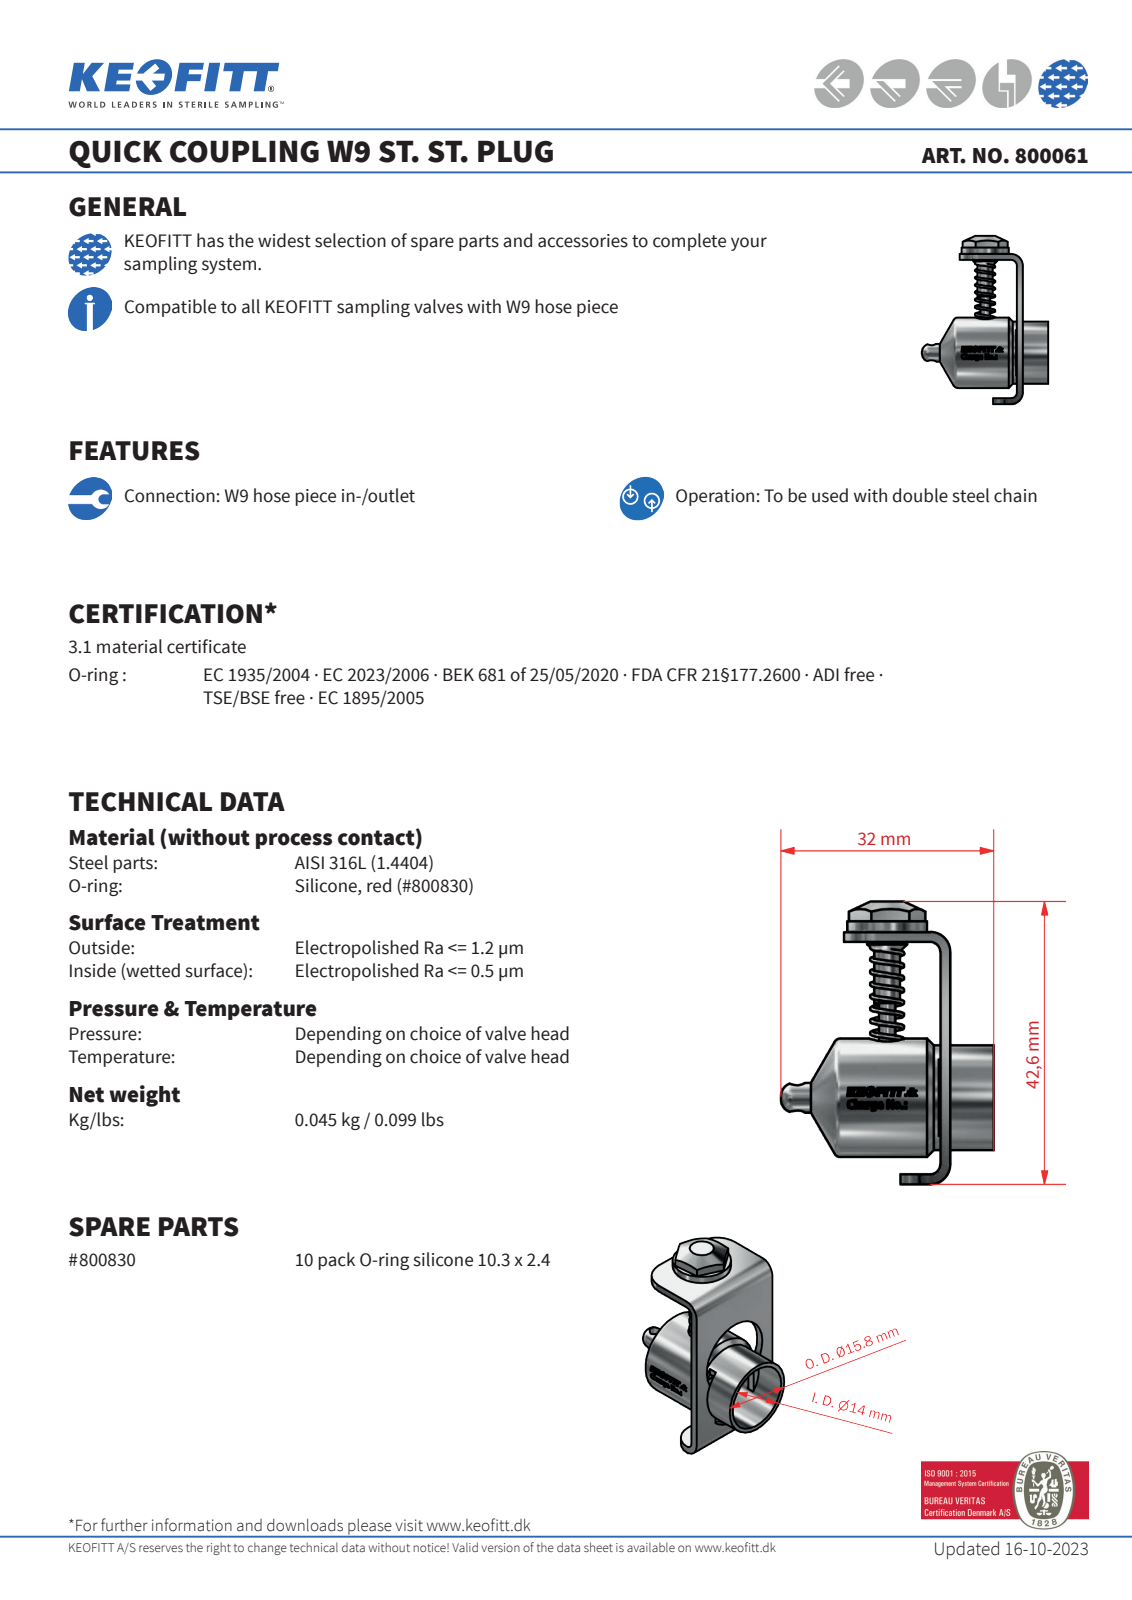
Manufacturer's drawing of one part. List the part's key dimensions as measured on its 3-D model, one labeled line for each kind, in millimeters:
Part name (STEP PRODUCT): 800061
STEP written by: Autodesk Inventor 2017 (AUTOMOTIVE_DESIGN)
Units: millimetres
Bodies: 1 solid, 80 faces (37 planar, 27 cylindrical, 16 other)
Overall size (bounding box): 42.6 × 32 × 22
Round holes (diameter × count): ⌀2.4 ×2, ⌀2.48 ×1, ⌀3 ×1, ⌀5.5 ×1, ⌀6.4 ×1, ⌀14 ×1, ⌀14.3 ×1
Round bosses / shafts (diameter × count): ⌀17.85 ×1, ⌀15.8 ×1, ⌀12 ×1, ⌀6 ×1, ⌀4.5 ×1, ⌀3.9 ×1, ⌀2.5 ×1
Partial cylindrical surfaces — rounded edges, fillets, slot ends (radius × count): R5 ×4, R1.5 ×2, R3 ×2, R8.05 ×1, R8.08 ×1
Main face-to-face distances: 1.5, 36.5, 7.5, 6, 38, 35, 22, 6.5, 8, 14
Hole centre spacings: 13.5
